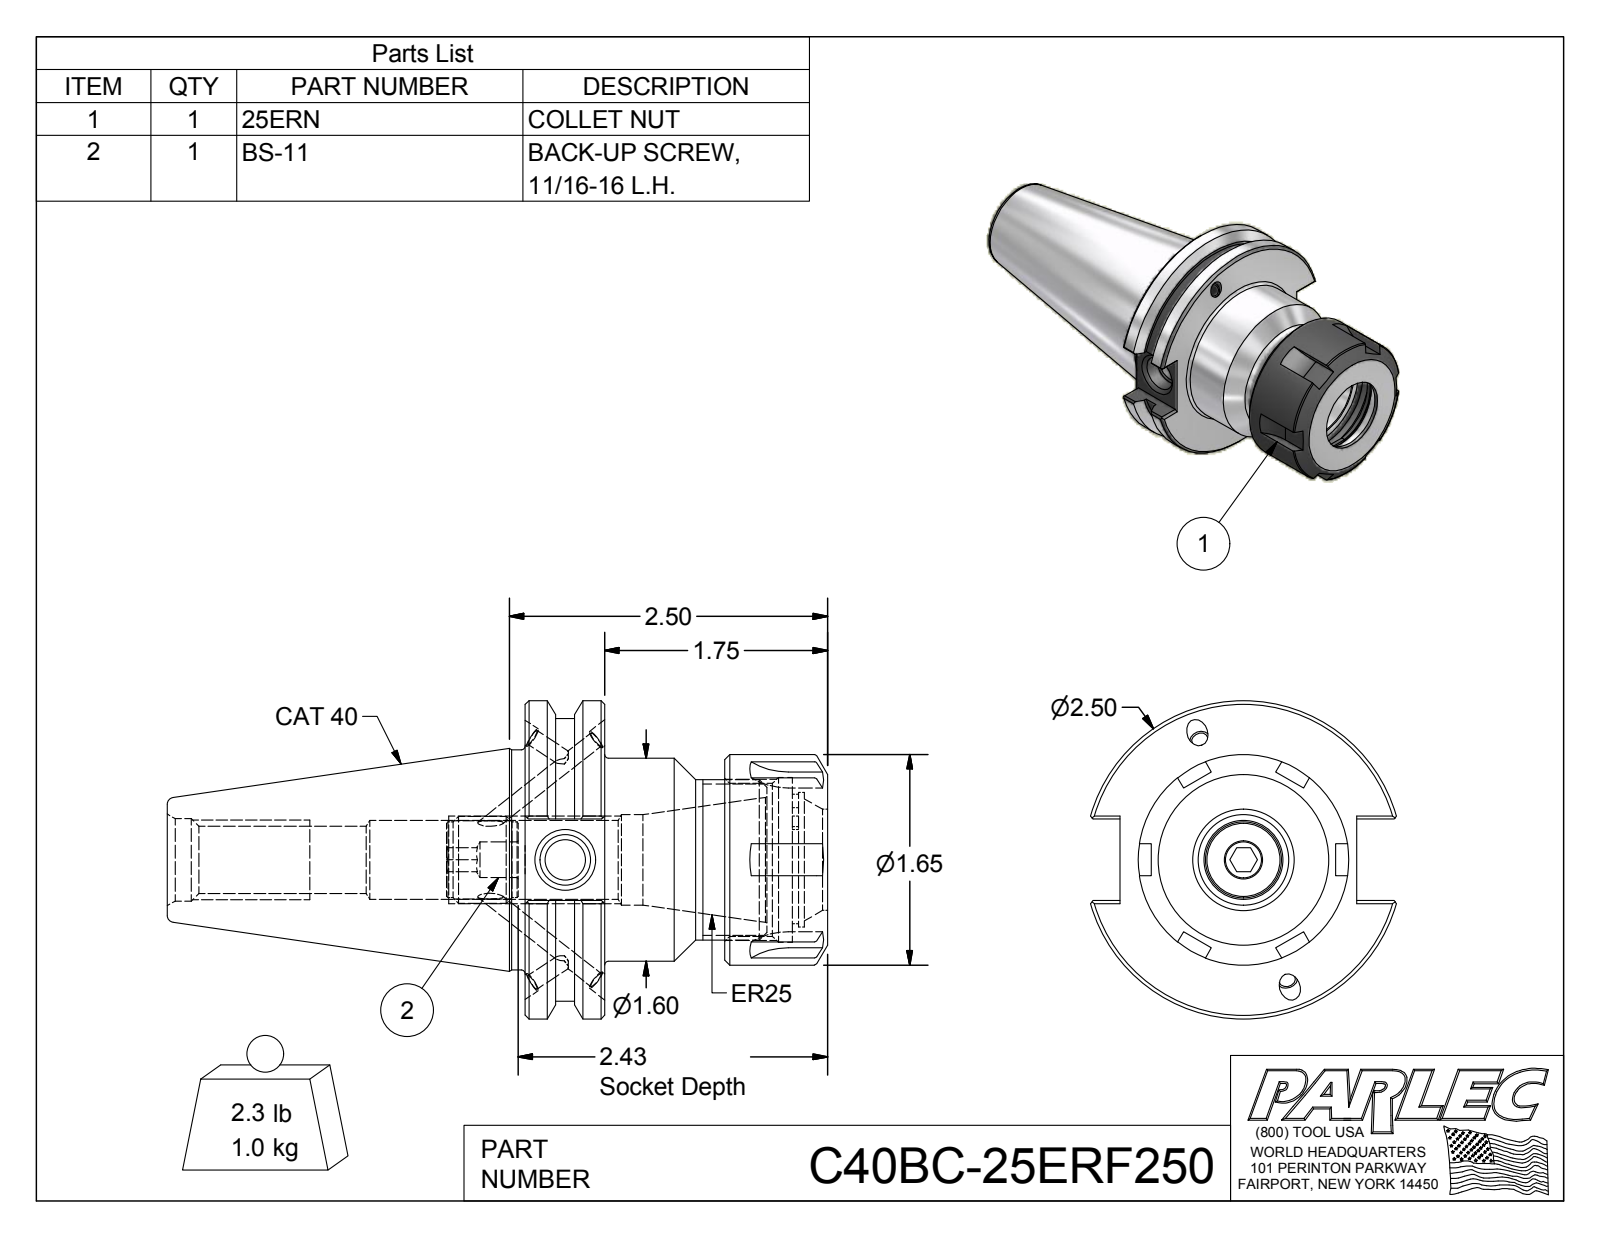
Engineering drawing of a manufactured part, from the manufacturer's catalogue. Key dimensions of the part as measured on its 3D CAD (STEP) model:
Part name (STEP PRODUCT): C40BCB-25ER2-1; 029-965; BS-11; 25ERN (+1 more)
STEP written by: Autodesk Inventor 2016 (AUTOMOTIVE_DESIGN)
Units: millimetres
Bodies: 7 solids, 251 faces (118 planar, 58 cylindrical, 75 other)
Overall size (bounding box): 131.76 × 63.5 × 61.05
Volume: 136 250 mm³ · Surface area: 34 854 mm²
Round holes (diameter × count): ⌀3.3 ×4, ⌀4.1 ×4, ⌀7.11 ×1, ⌀8 ×1, ⌀10.05 ×1, ⌀13.39 ×1, ⌀15.75 ×1, ⌀16.46 ×1, ⌀18.03 ×1, ⌀20.32 ×1, ⌀30.5 ×1, ⌀32.88 ×1
Round bosses / shafts (diameter × count): ⌀4.2 ×4, ⌀4 ×4, ⌀63.5 ×1, ⌀56.36 ×1, ⌀43.94 ×1, ⌀42 ×1, ⌀40.51 ×1, ⌀32 ×1
Partial cylindrical surfaces — rounded edges, fillets, slot ends (radius × count): R0.51 ×12, R12 ×1, R13.06 ×1, R13.43 ×1
Main face-to-face distances: 15.87, 60.32, 44.45, 39.75, 23.88, 20.57, 53.22, 37.35, 13.47, 7.1
